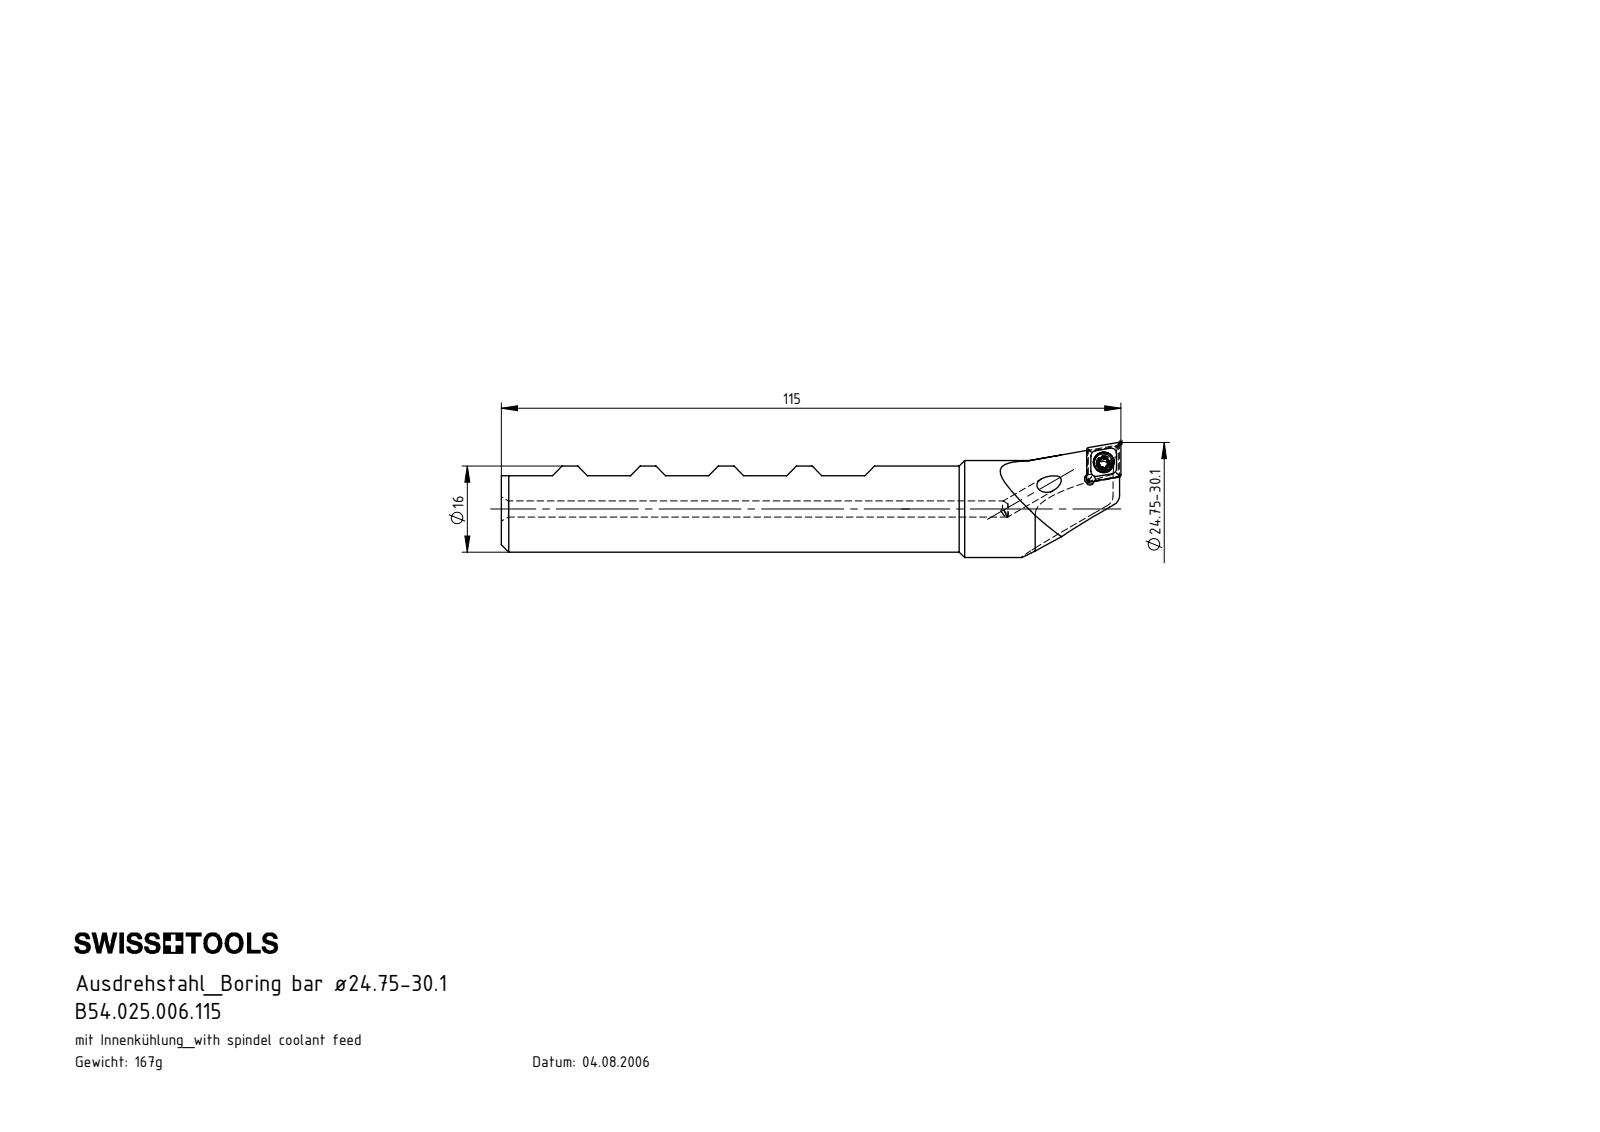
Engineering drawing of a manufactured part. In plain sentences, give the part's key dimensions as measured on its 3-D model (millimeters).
The part is named "WCA-ER2.001.006_A; B54.025.006.115; B25-WCA.K11.115_A_mit beschriftung; CCMT060204". Its 3-D file was written by "SolidWorks 2017 (CONFIG_CONTROL_DESIGN)". It is 3 solids with 166 faces: 42 planar, 68 cylindrical and 56 other. Overall it measures 115 by 21.38 by 18.92 millimeters. Its volume is 21 230 cubic millimeters and its surface area 7 292 square millimeters. Round holes: 2 of diameter 3, 1 of diameter 2, 1 of diameter 2.05, 1 of diameter 2.8, 1 of diameter 3.85. Round bosses or shafts: 1 of diameter 18, 1 of diameter 16, 1 of diameter 3.4, 1 of diameter 2.5. Partial cylindrical surfaces (rounded edges, fillets, slot ends): 6 of radius 0.21, 5 of radius 0.36, 1 of radius 0.36, 1 of radius 2, 1 of radius 9.2, 1 of radius 12. The main face-to-face distances are 10.25, 7.9, 20.5, 10.08, 2.18, 20.51, 30.76, 30.75, 10.26, 41.01. The hole center spacings are 3.89, 3.99.
